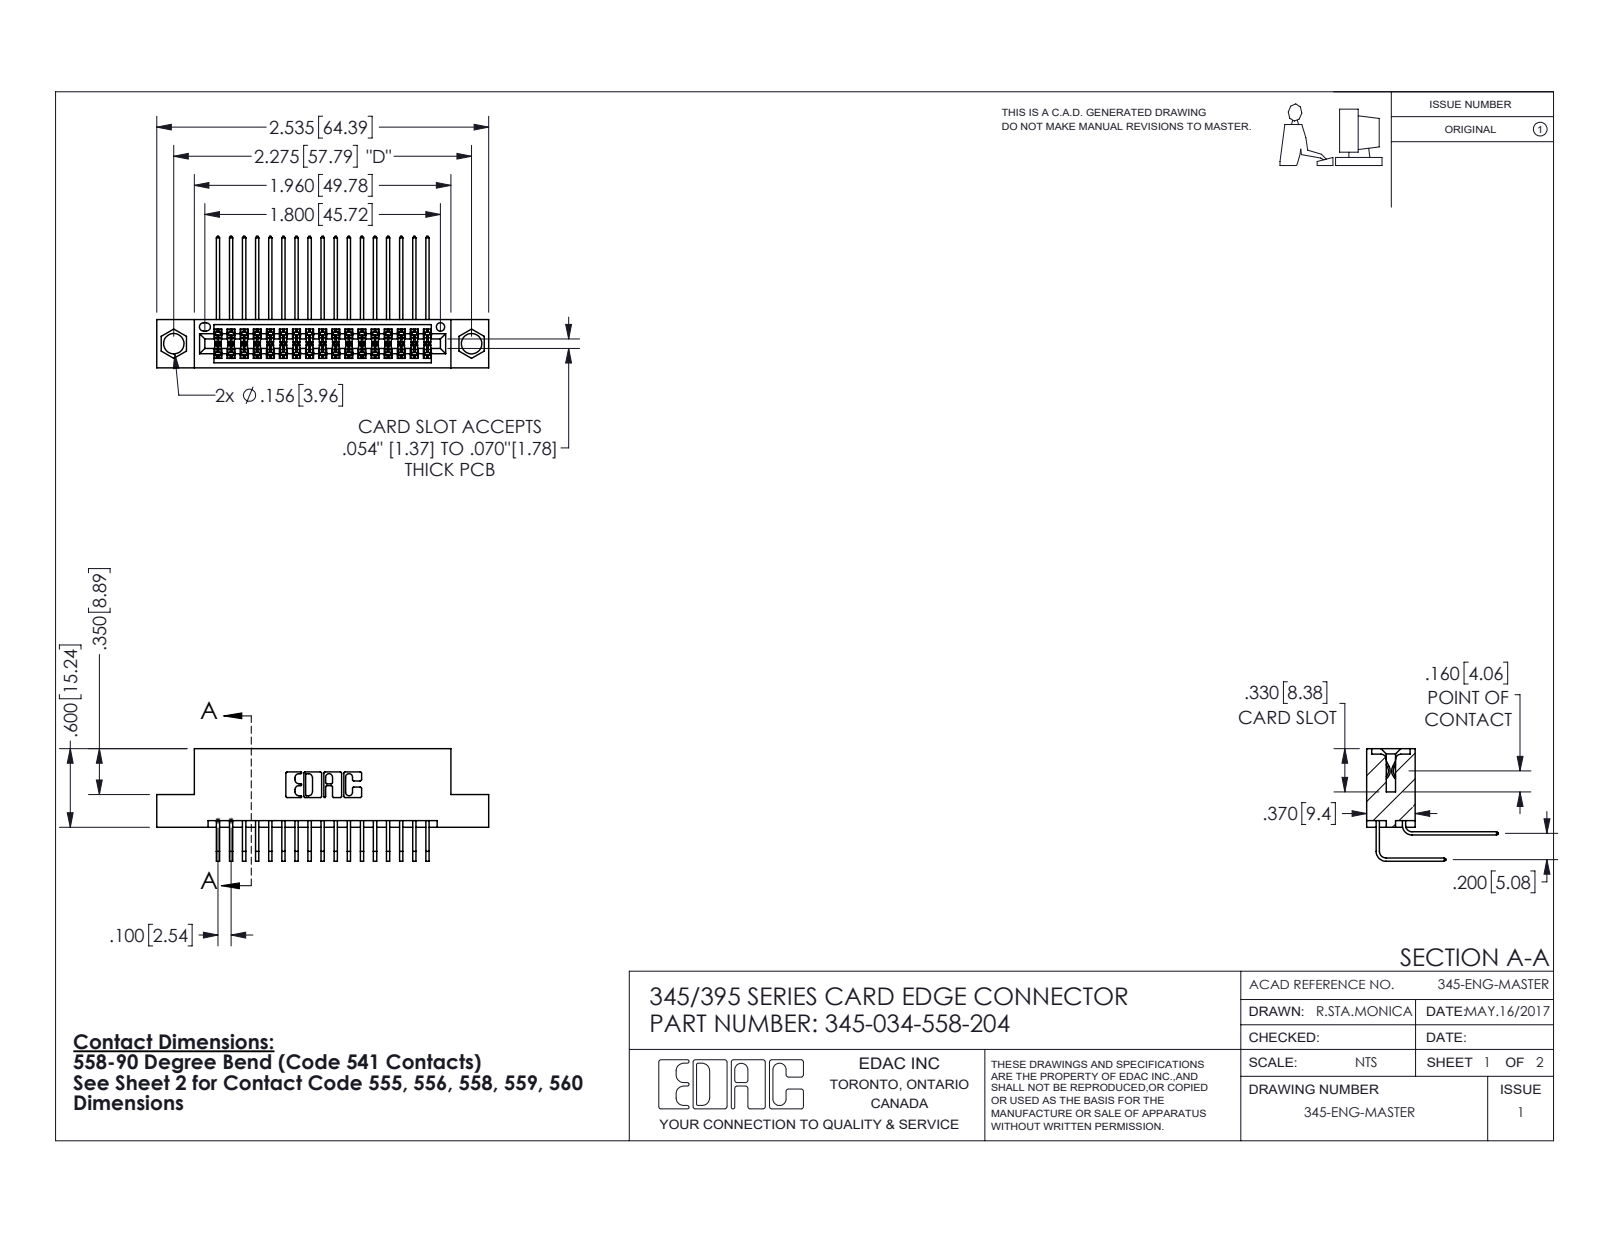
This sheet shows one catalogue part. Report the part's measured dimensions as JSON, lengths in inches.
{"part_name": "345-292-001_558 559 Tail - 1; 345 Part_Flush Mounting Lugs - 0.156 Dia-TI; 345-292-001_558 Tail - 2; 345-034-558-204", "step_written_by": "SolidWorks 2020 (CONFIG_CONTROL_DESIGN)", "units": "inches", "bodies": {"solids": 35, "faces": 1908, "planar": 1284, "cylindrical": 624, "other": 0}, "overall_size": [2.535, 1.005, 0.859], "volume_in3": 0.373, "surface_area_in2": 14.45, "round_holes": [[0.156, 2], [0.064, 1]], "partial_cylinders_radius": [[0.006, 67], [0.01, 22], [0.007, 6], [0.031, 6], [0.026, 3], [0.014, 2], [0.019, 2], [0.022, 2]], "face_to_face_distances": [0.2, 0.072, 0.298, 0.37, 0.098, 0.272, 0.025, 0.225, 0.1, 0.285], "hole_center_spacings": [0.27, 2.041, 2.275]}
